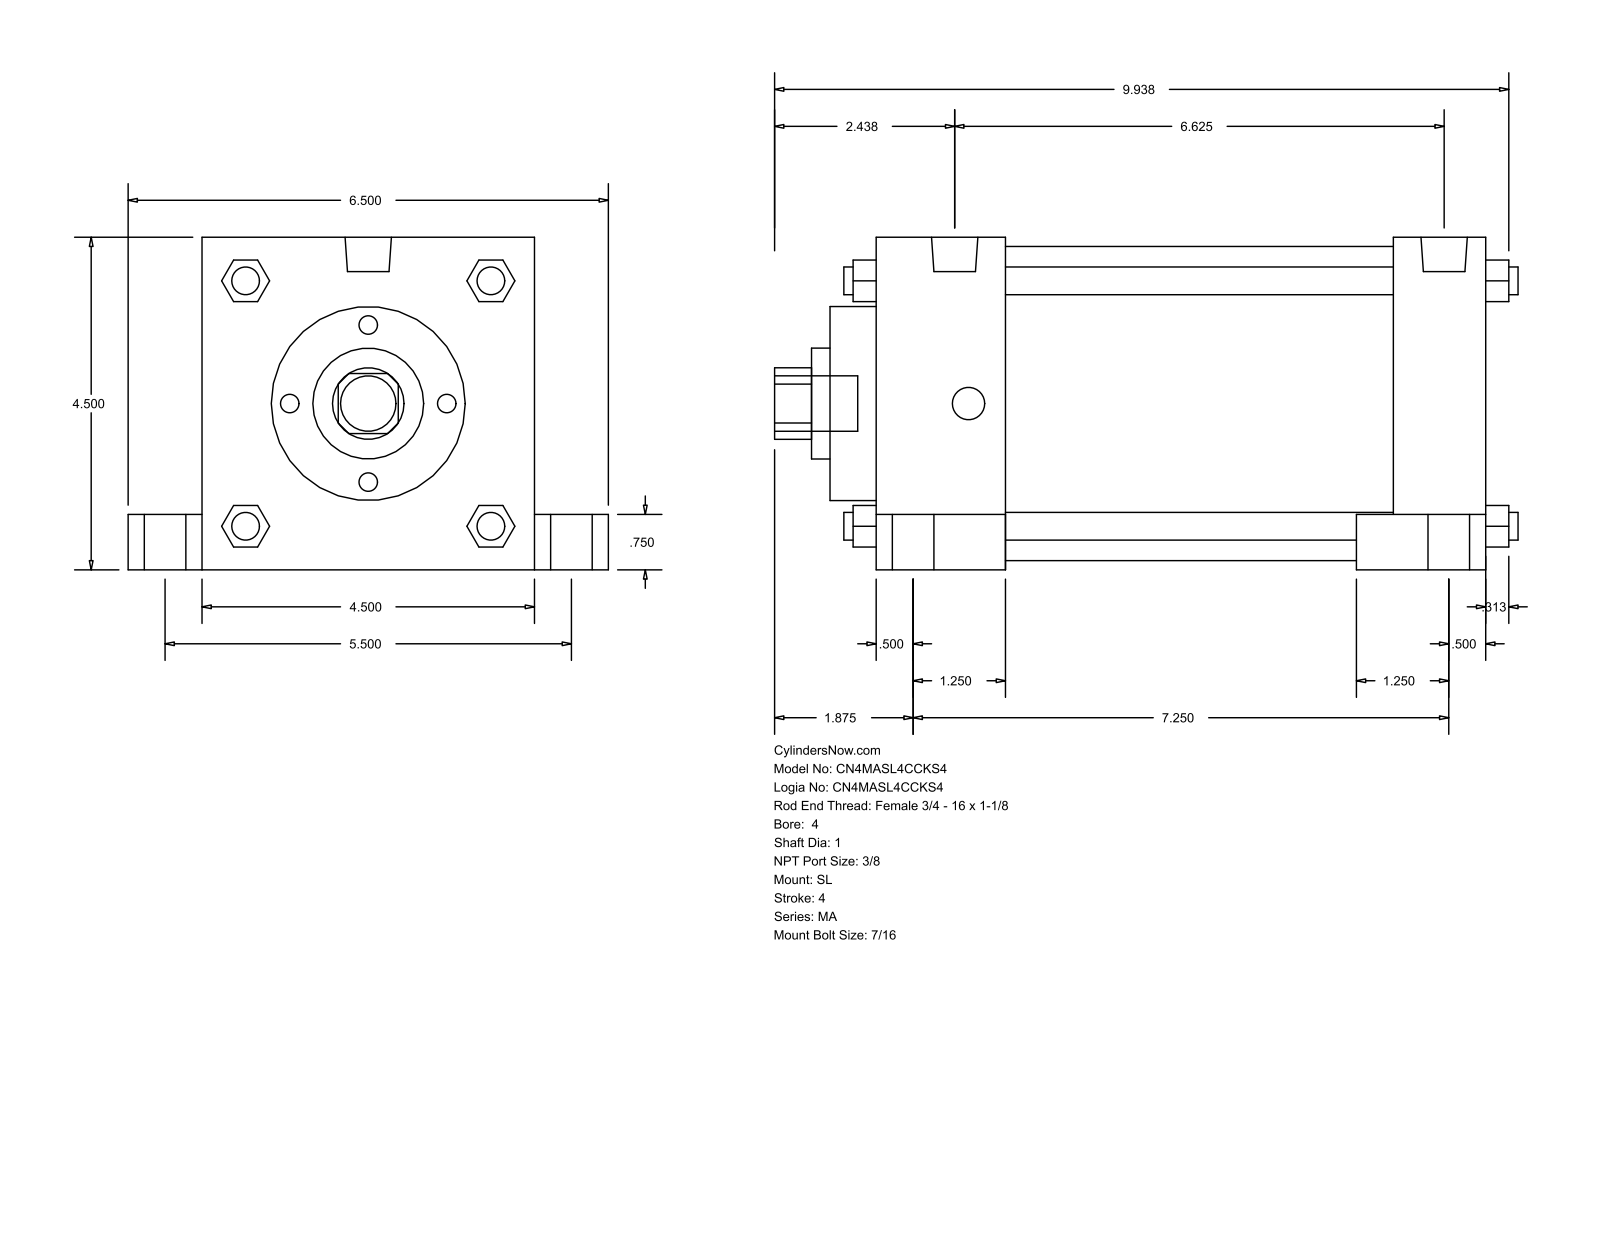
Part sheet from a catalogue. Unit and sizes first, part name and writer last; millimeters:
Units: millimetres
Overall size (bounding box): 255.59 × 165.1 × 114.3
Round holes (diameter × count): ⌀25.4 ×1, ⌀38.1 ×1, ⌀66.67 ×1, ⌀107.95 ×1
Round bosses / shafts (diameter × count): ⌀20.64 ×4, ⌀14.29 ×4, ⌀11.11 ×4, ⌀9.53 ×4, ⌀15.93 ×2, ⌀19.05 ×1
Partial cylindrical surfaces — rounded edges, fillets, slot ends (radius × count): R12.29 ×1
Main face-to-face distances: 114.3, 209.55, 44.46, 165.09, 177.8, 133.34, 31.75, 25.4, 139.7, 225.42
Bodies: 0 solids, 150 faces (113 planar, 37 cylindrical, 0 other)
Part name (STEP PRODUCT): MA_SL__0400_1
STEP written by: GSSL Pune (CONFIG_CONTROL_DESIGN)
